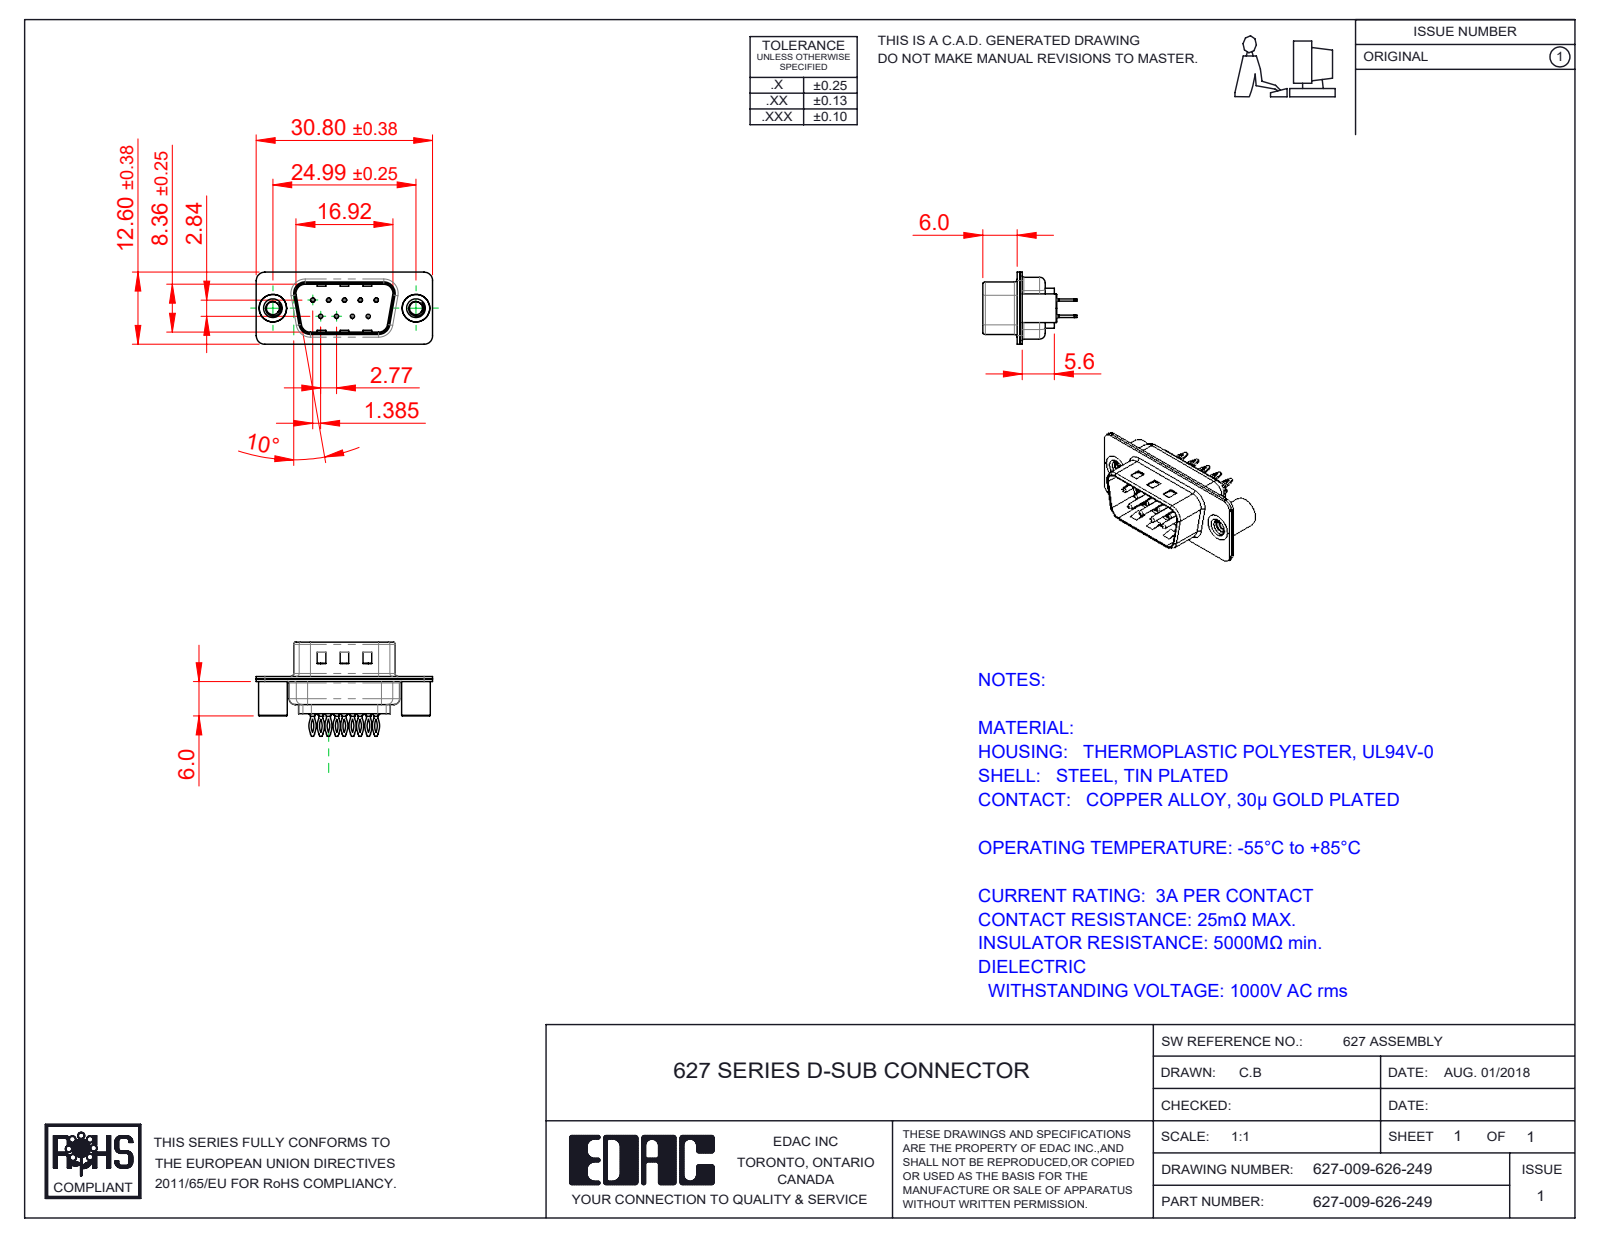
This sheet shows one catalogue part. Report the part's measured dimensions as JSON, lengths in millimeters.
{"part_name": "627 Shell Front_09 Contacts; 627 Contact Row 1_26L; 627 Shell Rear_09 Contacts; 627 Housing_09 LP (+3 more)", "step_written_by": "SolidWorks 2020 (CONFIG_CONTROL_DESIGN)", "units": "millimeters", "bodies": {"solids": 14, "faces": 1010, "planar": 287, "cylindrical": 428, "other": 295}, "overall_size": [30.8, 16.45, 12.6], "volume_mm3": 1408, "surface_area_mm2": 4096, "round_holes": [[0.35, 9], [1.1, 9], [1.6, 9], [2.26, 2], [4, 2], [4.8, 2]], "round_bosses_or_shafts": [[2, 9], [1.5, 9], [0.75, 9], [5, 2], [4.9, 2]], "partial_cylinders_radius": [[1.5, 18], [2.92, 18], [3.33, 18], [2, 12], [0.5, 8], [1.6, 8], [0.25, 4], [0.6, 4]], "face_to_face_distances": [0.4, 0.45, 0.9, 0.82, 9.58, 1.4, 8.76, 6.5, 0.5, 1.5], "hole_center_spacings": [3.16, 2.77, 5.54, 5.03, 5.04, 8.31, 7.48, 7.49]}
